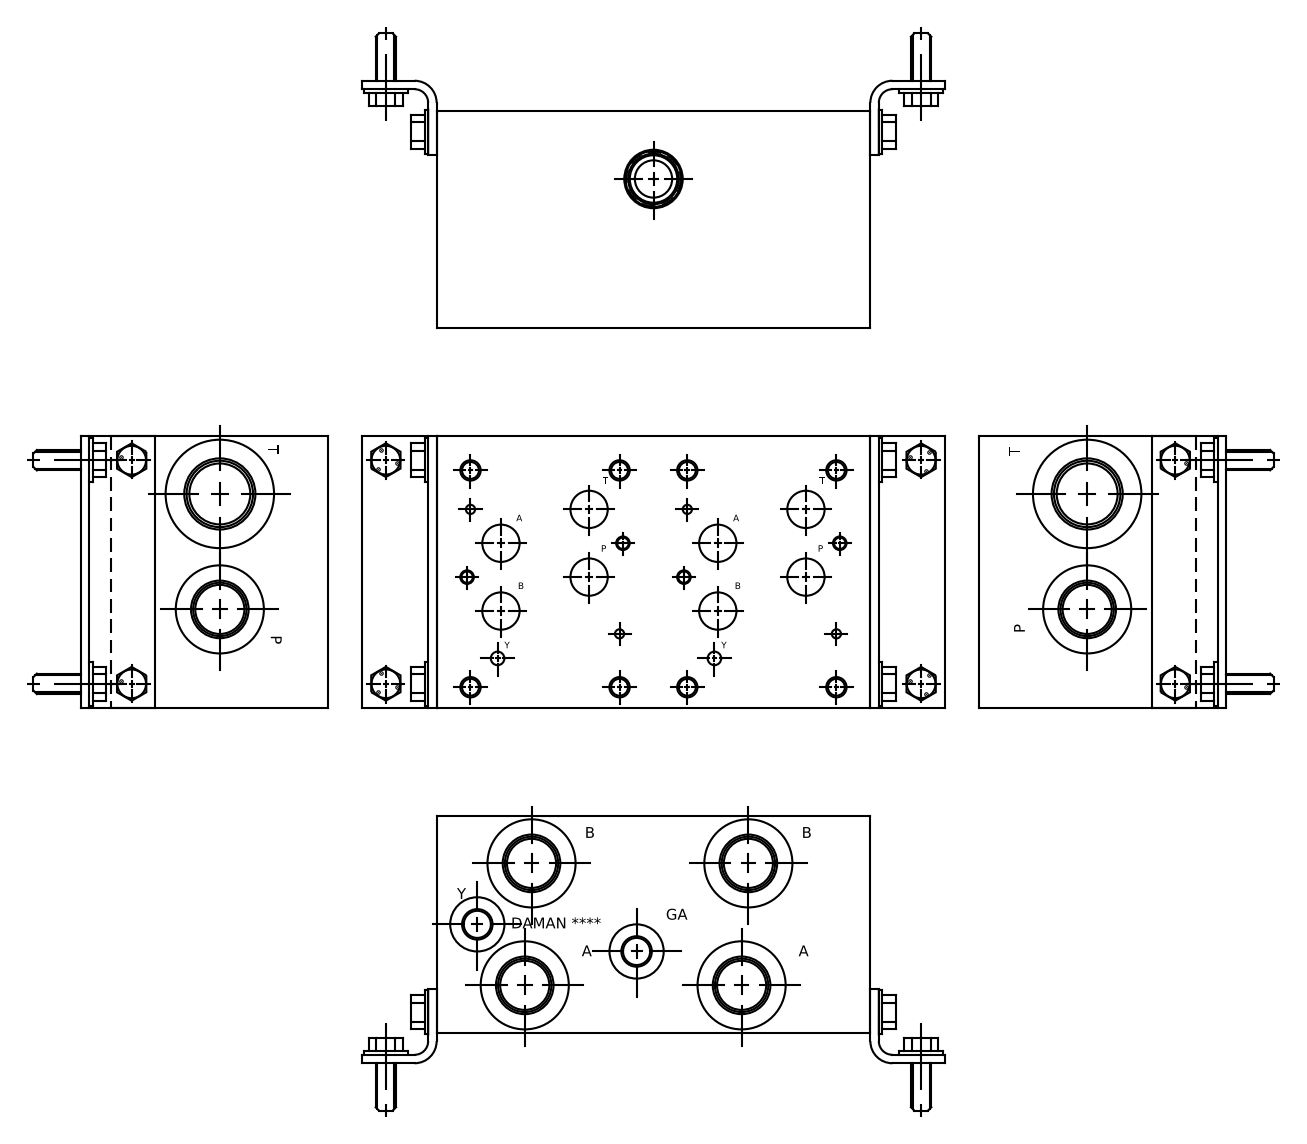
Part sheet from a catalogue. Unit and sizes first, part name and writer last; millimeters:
Units: millimetres
Overall size (bounding box): 203.2 × 127 × 101.6
Round holes (diameter × count): ⌀7.92 ×10, ⌀9.53 ×10, ⌀17.48 ×5, ⌀23.01 ×5, ⌀24.92 ×5, ⌀27.43 ×5, ⌀42.04 ×5, ⌀4.37 ×4, ⌀5.11 ×4, ⌀6.35 ×4, ⌀16.66 ×4, ⌀26.99 ×3
Main face-to-face distances: 101.6, 127, 203.2, 0.79, 126.21, 202.41, 201.62, 19.05, 19.84, 183.36
Hole centre spacings: 101.6, 44.22, 101.59, 31.75, 22.45, 22.46, 57.15, 65.38
Volume: 2 385 000 mm³ · Surface area: 161 791 mm²
Bodies: 1 solid, 705 faces (378 planar, 103 cylindrical, 224 other)
Part name (STEP PRODUCT): Part_DD07P024S~S_3D
STEP written by: Autodesk Inventor 2019 (AUTOMOTIVE_DESIGN)
